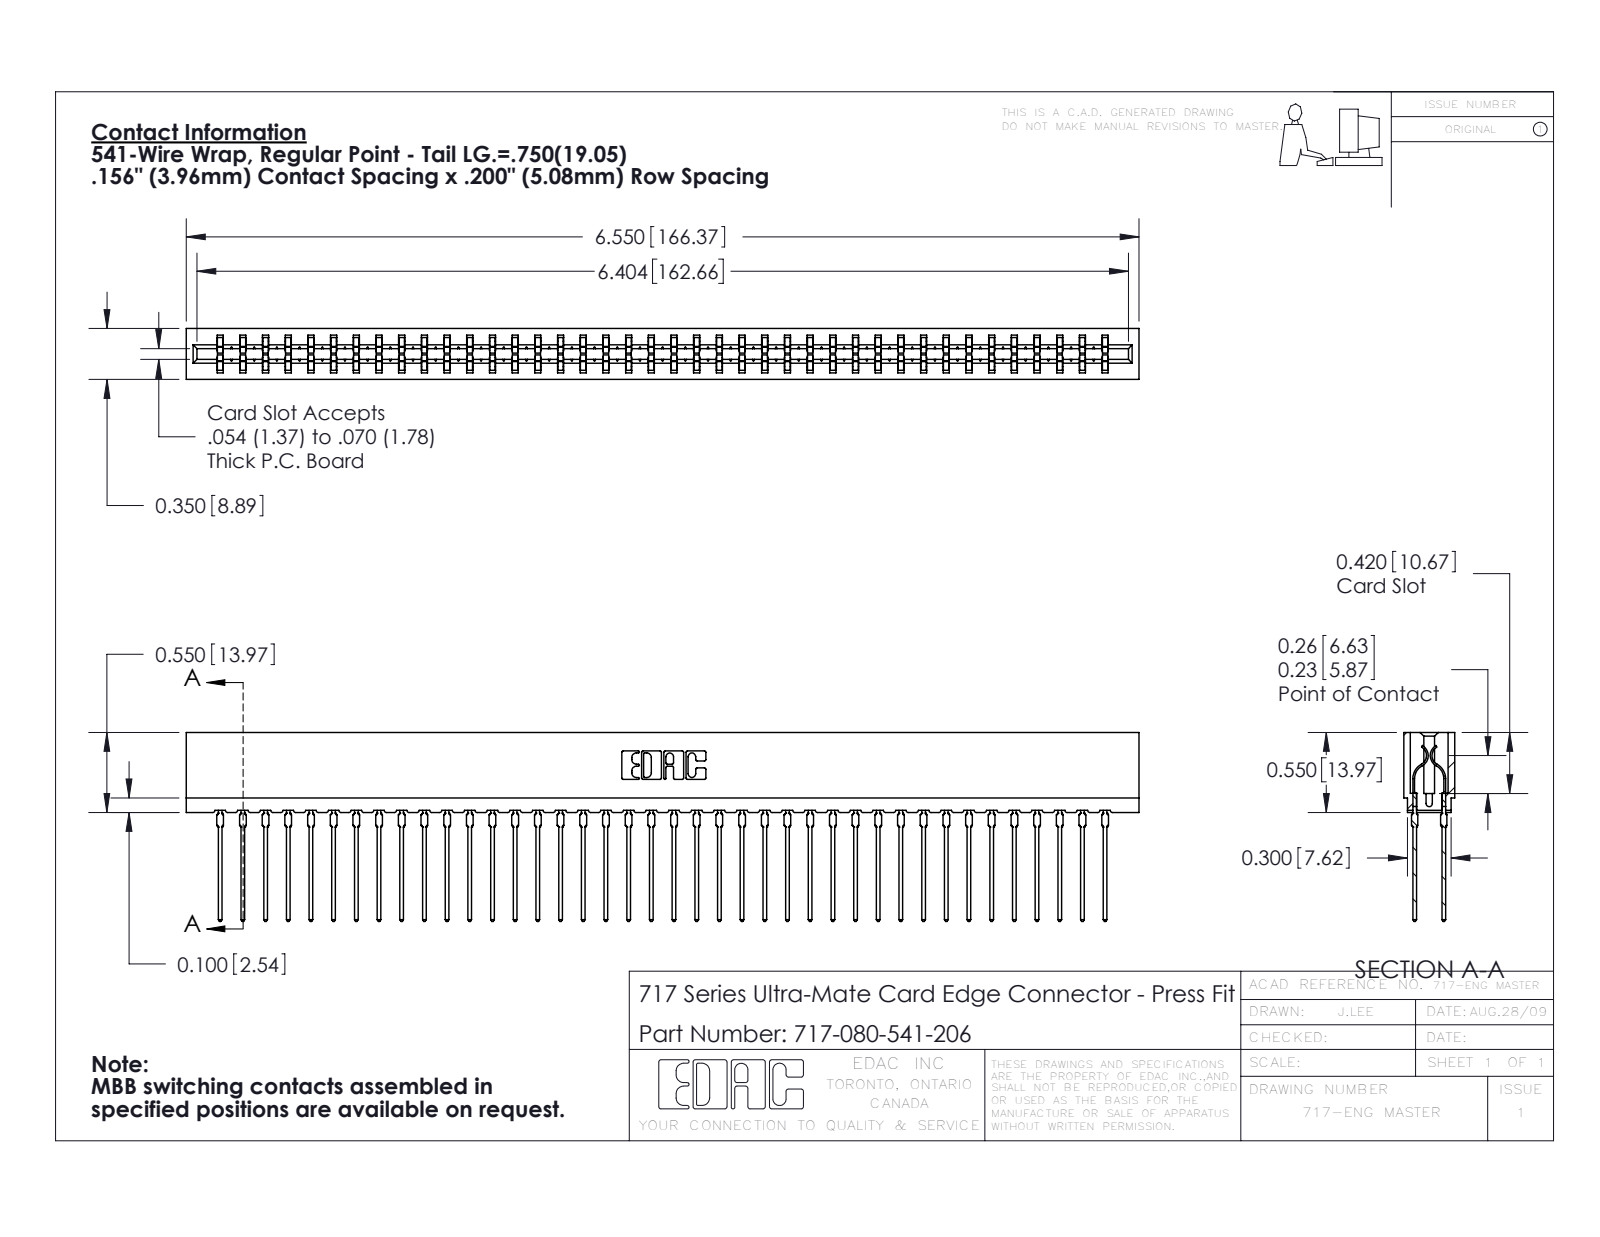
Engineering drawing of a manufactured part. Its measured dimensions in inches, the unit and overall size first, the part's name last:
Units: inches
Overall size (bounding box): 6.55 × 1.299 × 0.35
Partial cylindrical surfaces — rounded edges, fillets, slot ends (radius × count): R0.021 ×160, R0.015 ×80, R0.01 ×22, R0.005 ×8, R0.011 ×8, R0.007 ×6, R0.031 ×6, R0.026 ×3
Main face-to-face distances: 0.212, 0.138, 0.35, 0.063, 0.287, 0.076, 0.149, 0.087, 0.263, 0.025
Volume: 0.904 in³ · Surface area: 37.85 in²
Bodies: 81 solids, 7294 faces (3774 planar, 1440 cylindrical, 2080 other)
Part name (STEP PRODUCT): 717 Part_Insulator Option - 06; 745-292-001_541; 717-080-541-206
STEP written by: SolidWorks 2016 (CONFIG_CONTROL_DESIGN)
